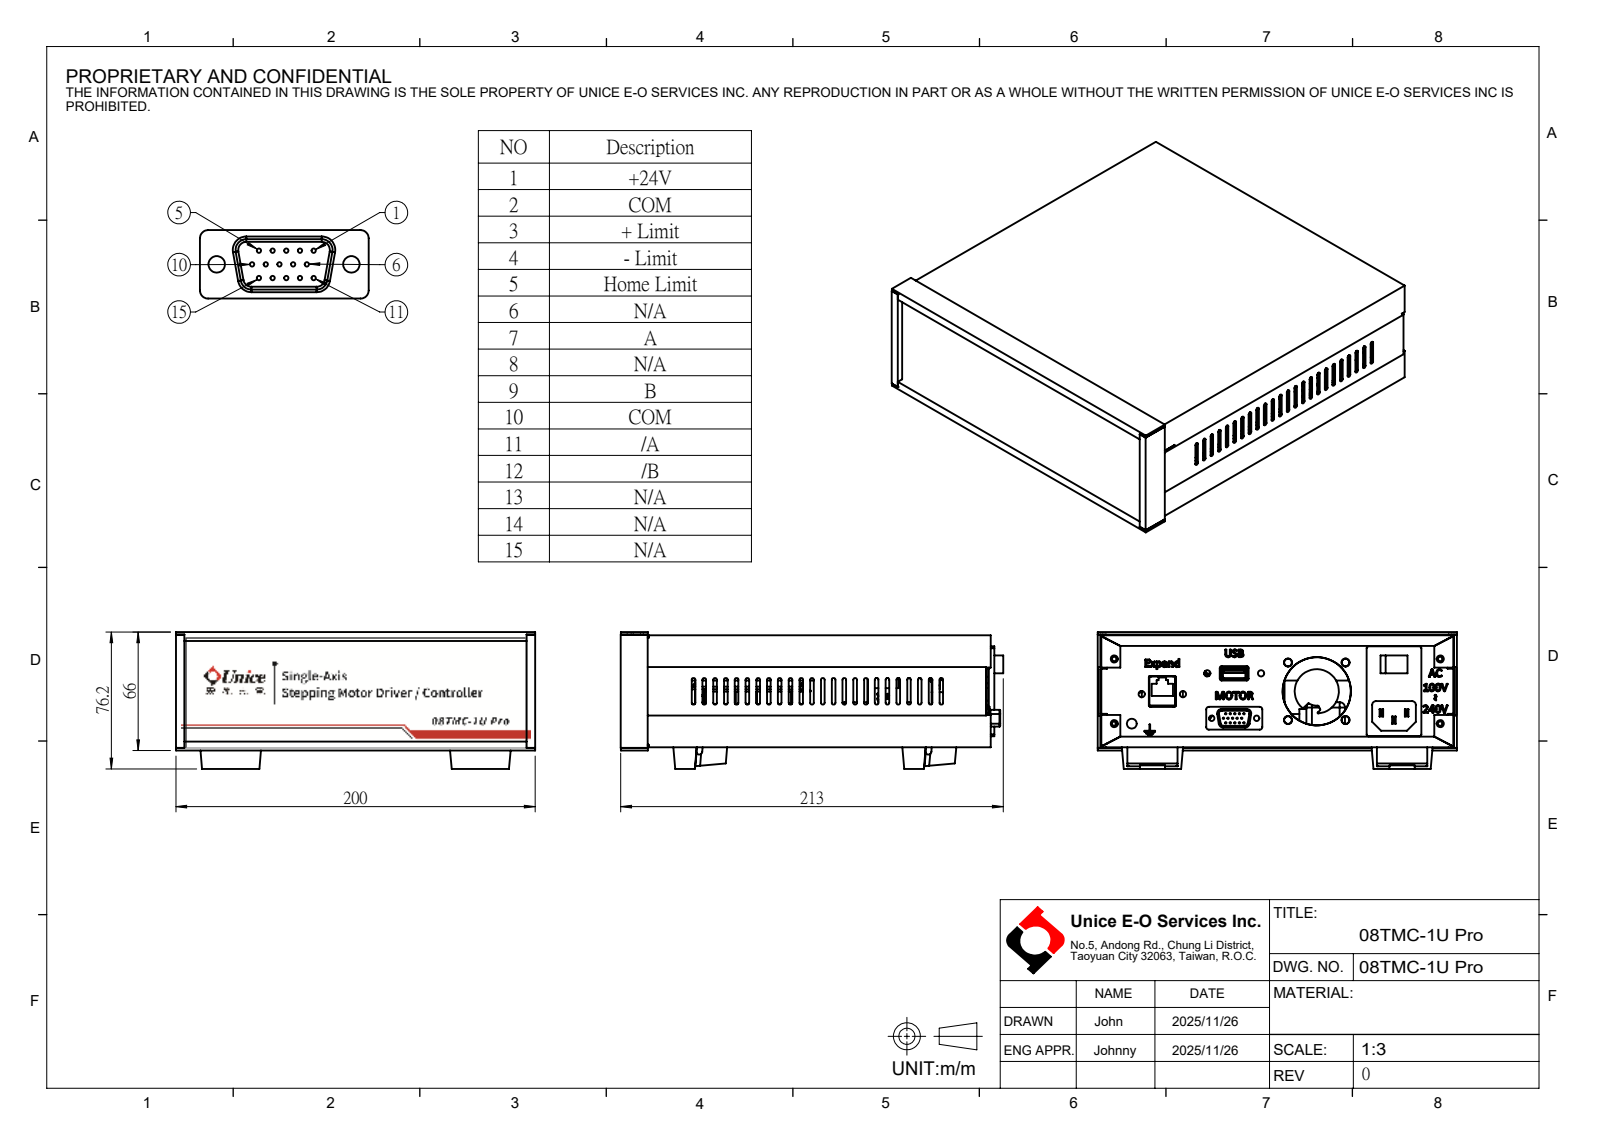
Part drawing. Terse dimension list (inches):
name: 08TMC-1U Pro
written by: SolidWorks 2024 (CONFIG_CONTROL_DESIGN)
unit: in
bodies: 0 solids, 773 faces (471 planar, 269 cylindrical, 33 other)
size: 8.386 × 7.874 × 3
holes: 15× ⌀0.031, 8× ⌀0.138, 6× ⌀0.098, 6× ⌀0.157, 4× ⌀0.169, 4× ⌀0.177, 2× ⌀0.12, 2× ⌀0.165, 1× ⌀0.197, 1× ⌀0.217, 1× ⌀0.472, 1× ⌀1.496
rounds: 56× R0.039, 12× R0.059, 8× R0.02, 8× R0.079, 5× R0.008, 4× R0.124, 3× R0.024, 2× R0.065
face distances: 0.039, 2.417, 0.244, 2.173, 2.378, 2.457, 0.283, 0.205, 2.213, 2.134
hole spacings: 0.112, 0.2, 0.18, 0.1, 0.224, 0.269, 0.283, 0.3
